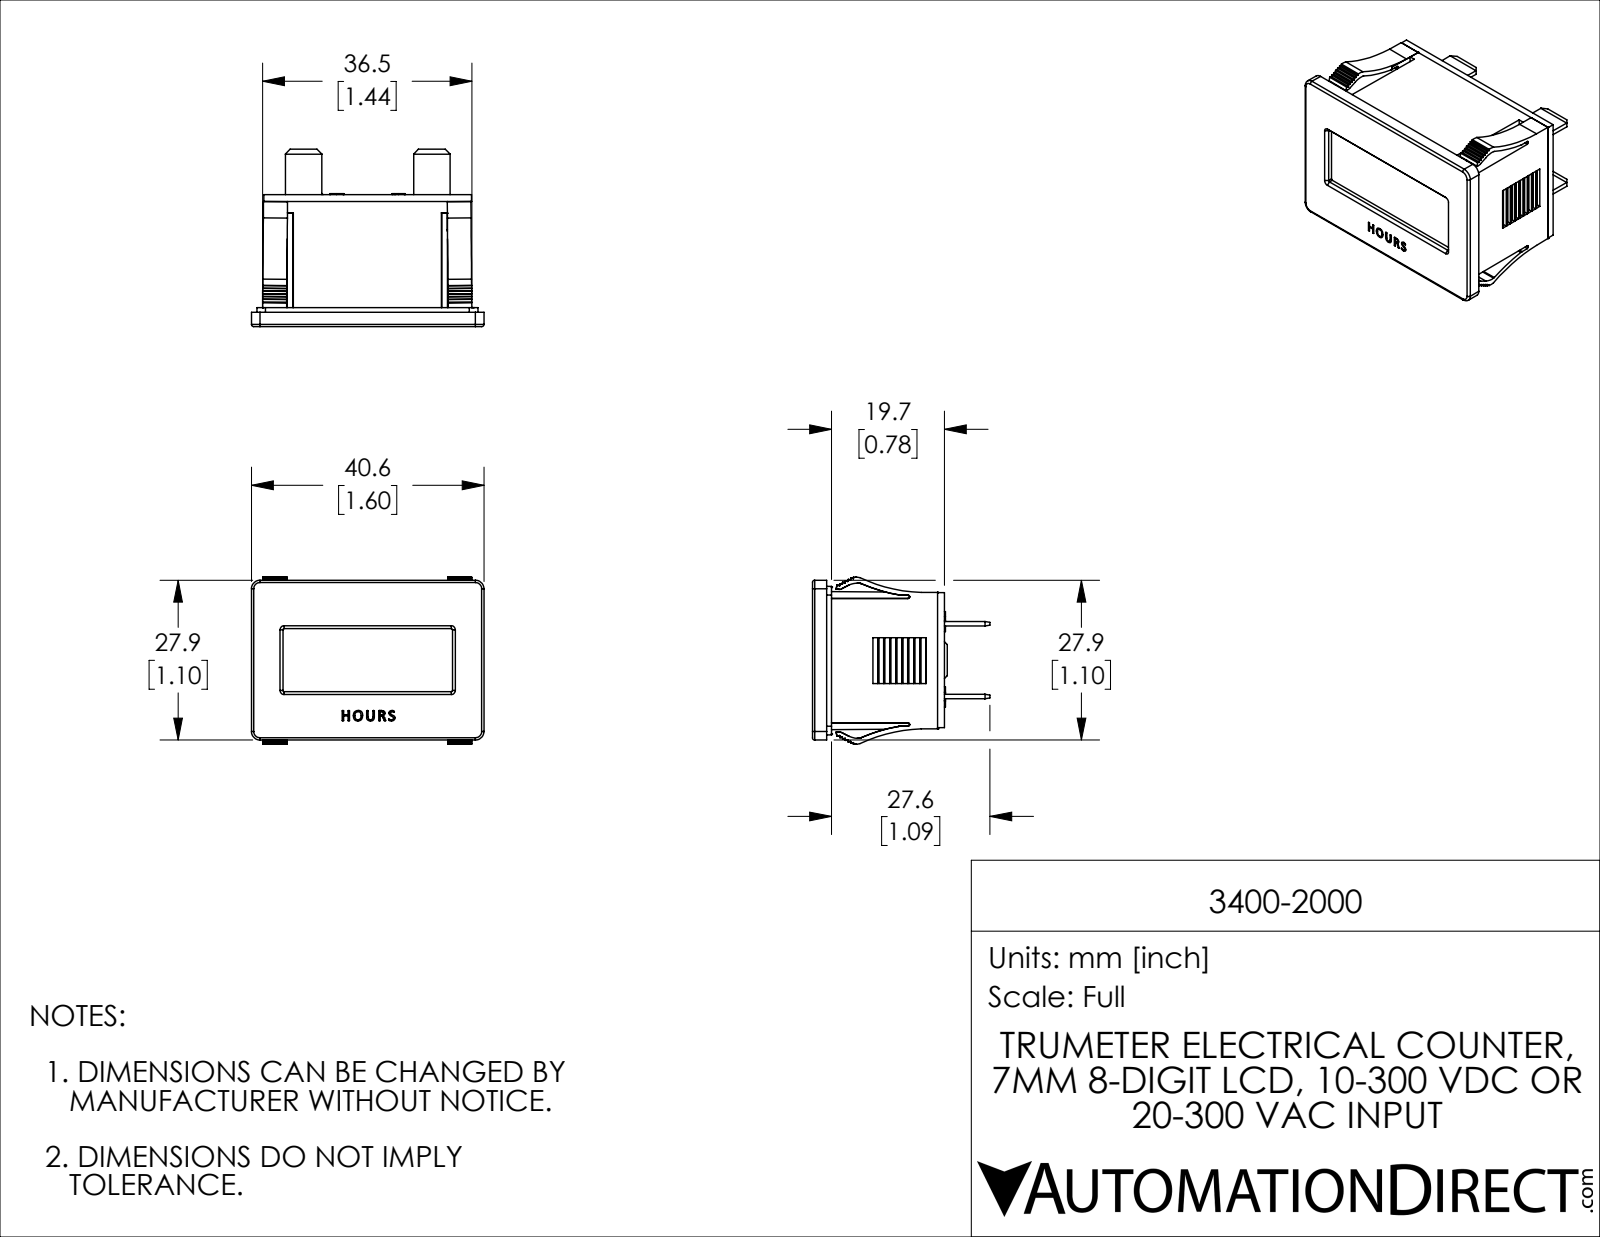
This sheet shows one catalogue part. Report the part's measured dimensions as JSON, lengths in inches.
{"part_name": "3400-2000", "step_written_by": "SolidWorks 2021 (CONFIG_CONTROL_DESIGN)", "units": "inches", "bodies": {"solids": 1, "faces": 722, "planar": 496, "cylindrical": 78, "other": 148}, "overall_size": [1.598, 1.22, 1.148], "volume_in3": 1.234, "surface_area_in2": 12.16, "partial_cylinders_radius": [[0.059, 8], [0.01, 6], [0.008, 4], [0.016, 4], [0.03, 4], [0.006, 2], [0.01, 2], [0.015, 2]], "face_to_face_distances": [0.047, 0.86, 0.907, 0.048, 0.859, 0.031, 0.811, 0.813, 0.5, 0.828]}
